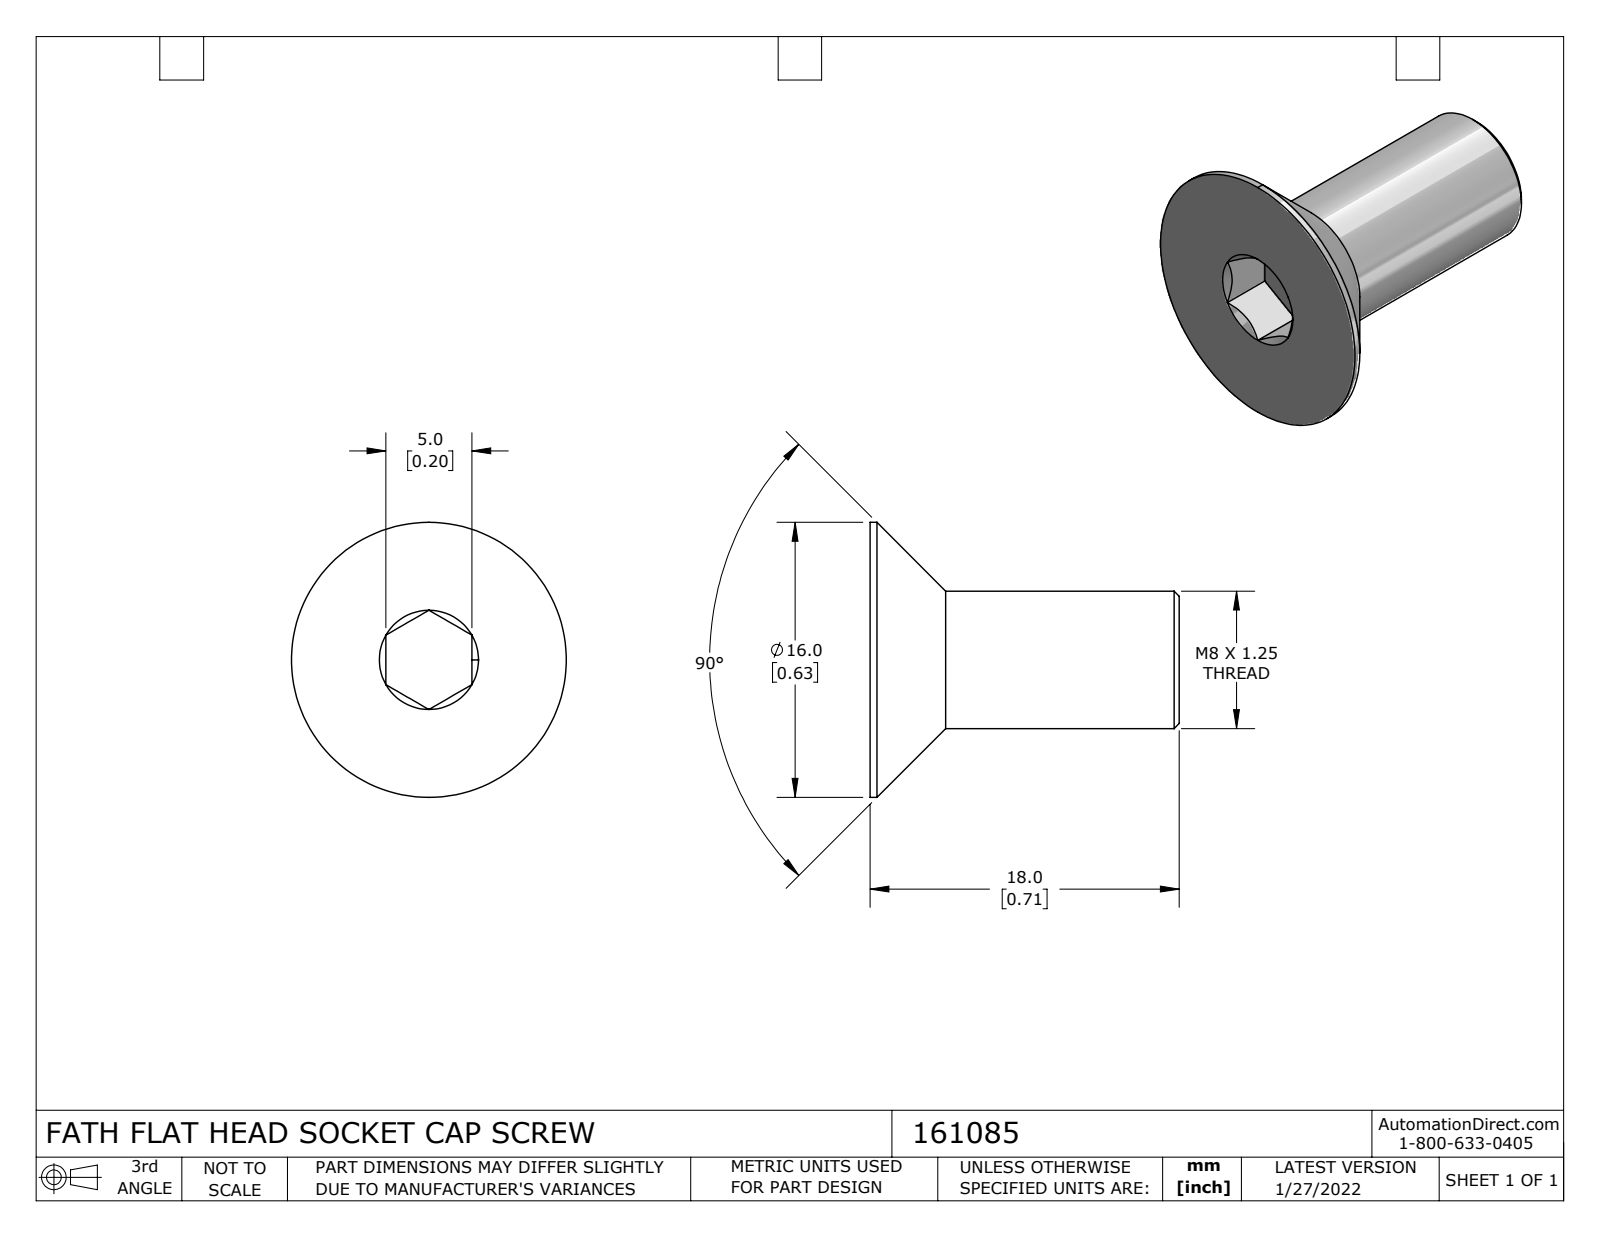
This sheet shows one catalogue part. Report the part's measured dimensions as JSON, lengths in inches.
{"part_name": "161085", "step_written_by": "SolidWorks 2021 (CONFIG_CONTROL_DESIGN)", "units": "inches", "bodies": {"solids": 1, "faces": 24, "planar": 9, "cylindrical": 4, "other": 11}, "overall_size": [0.709, 0.63, 0.63], "volume_in3": 0.071, "surface_area_in2": 1.35, "round_bosses_or_shafts": [[0.63, 1], [0.315, 1]], "face_to_face_distances": [0.709, 0.197, 0.587, 0.121]}
